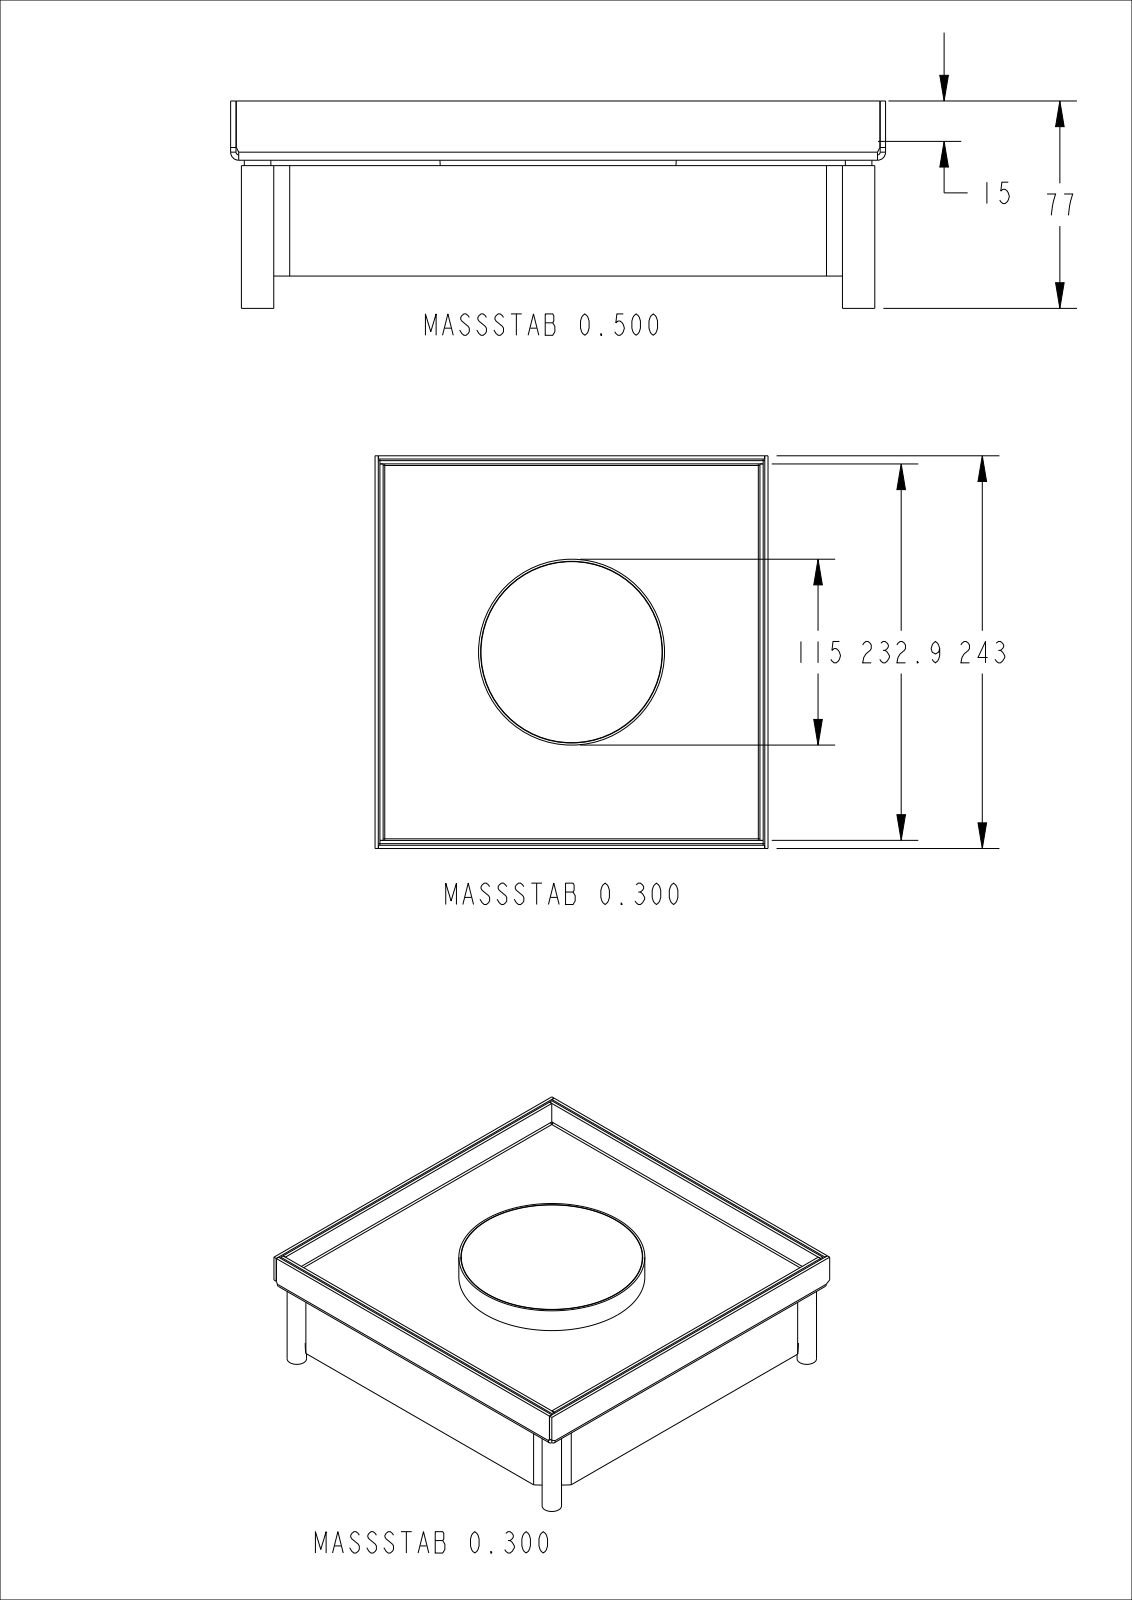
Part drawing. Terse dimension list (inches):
name: T-00626_1; T-00632_1; T-00625_1; T-00823_ASM_1_ASM (+8 more)
written by: CREO PARAMETRIC BY PTC INC, 2022281 (AUTOMOTIVE_DESIGN)
unit: in
bodies: 10 solids, 241 faces (138 planar, 93 cylindrical, 10 other)
size: 9.567 × 9.567 × 3.031
volume: 21.34 in³; area: 516.3 in²
holes: 4× ⌀0.268, 4× ⌀0.335, 3× ⌀0.177, 1× ⌀3.173, 1× ⌀3.543, 1× ⌀3.976, 1× ⌀4.213, 1× ⌀4.276, 1× ⌀4.409, 1× ⌀4.425
bosses: 4× ⌀0.472, 4× ⌀0.388, 1× ⌀4.528, 1× ⌀4.37, 1× ⌀4.134, 1× ⌀3.843
rounds: 8× R0.039, 8× R0.118, 3× R0.197, 1× R1.693, 1× R5.906, 1× R6.004
face distances: 0.079, 0.118, 0.098, 9.252, 0.197, 9.37, 9.035, 0.039, 9.134, 0.236
hole spacings: 6.208, 8.78, 2.126, 3.682, 4.191, 4.939, 6.019, 7.063
